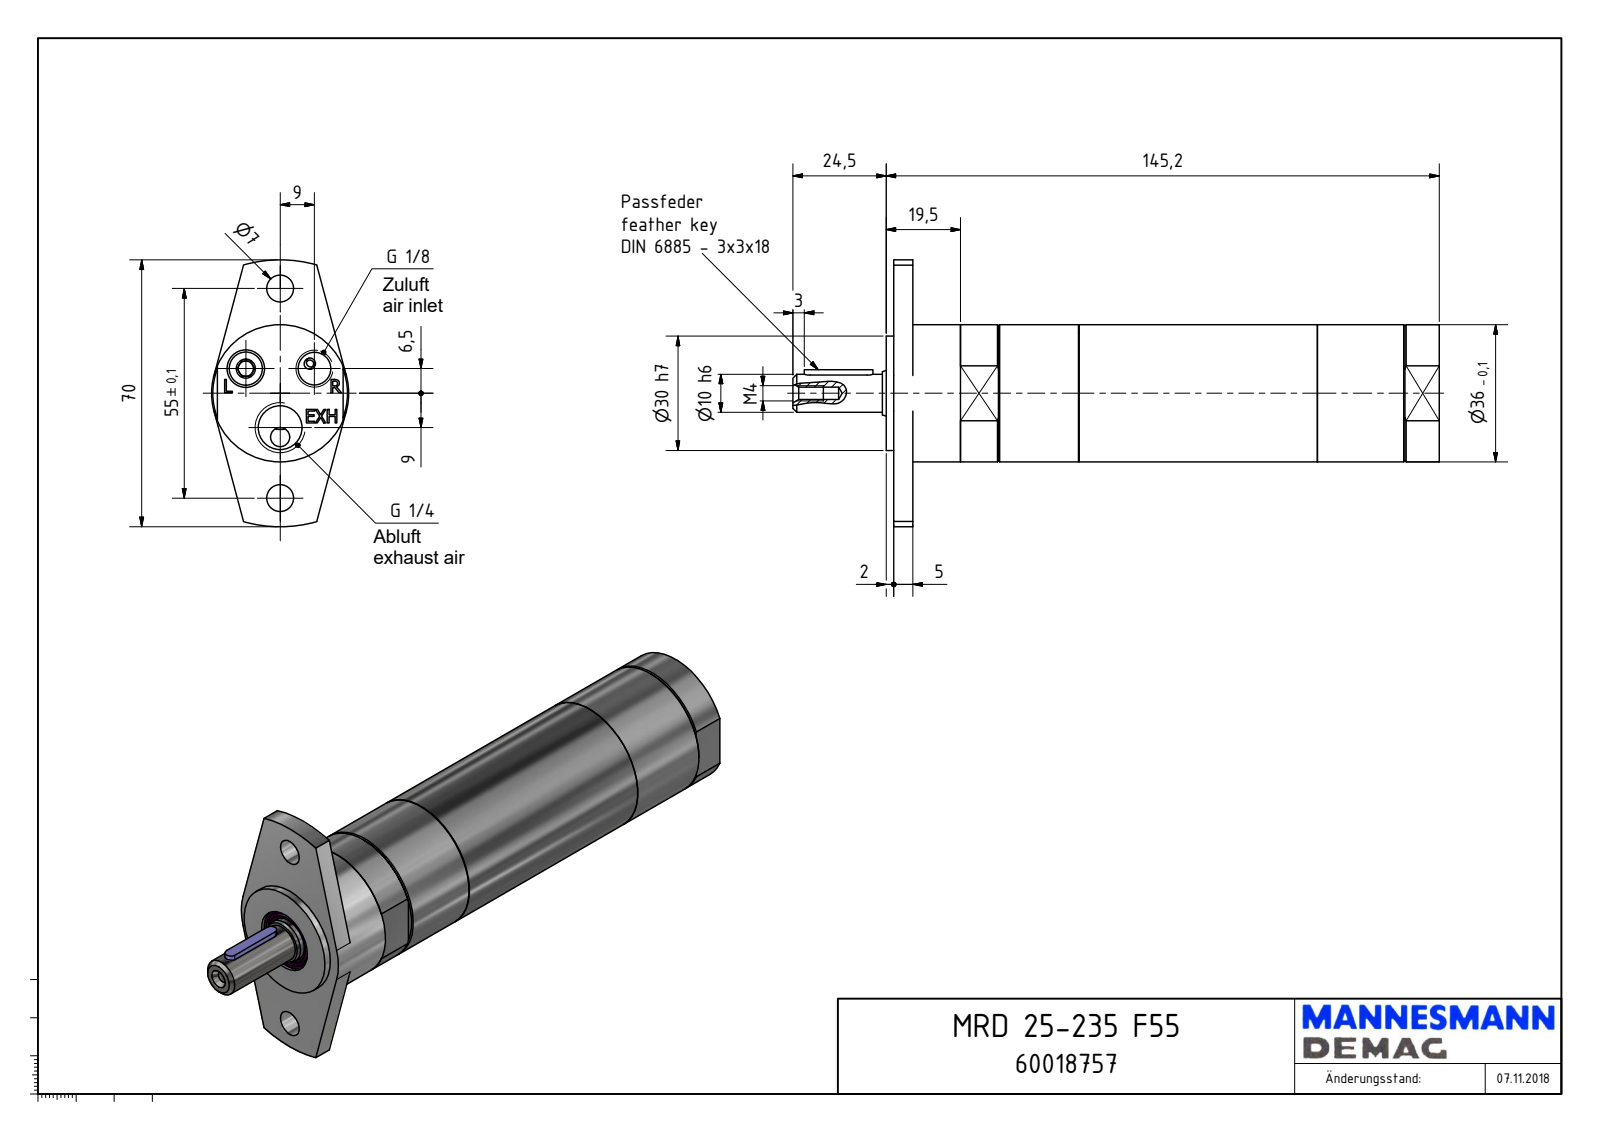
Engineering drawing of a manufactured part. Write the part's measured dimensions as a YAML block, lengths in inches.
part_name: "MRD 25-235 F55_60018757"
step_written_by: "Autodesk Inventor 2018 (AUTOMOTIVE_DESIGN)"
units: inches
bodies: {solids: 1, faces: 160, planar: 106, cylindrical: 27, other: 27}
overall_size: [6.681, 2.756, 1.417]
volume: 9.188
surface_area: 36.06
round_holes:
  - {diameter: 0.276, count: 2}
  - {diameter: 0.337, count: 2}
  - {diameter: 0.128, count: 1}
  - {diameter: 0.157, count: 1}
  - {diameter: 0.451, count: 1}
  - {diameter: 0.61, count: 1}
  - {diameter: 0.669, count: 1}
round_bosses_or_shafts:
  - {diameter: 1.417, count: 1}
  - {diameter: 1.26, count: 1}
  - {diameter: 1.181, count: 1}
  - {diameter: 0.47, count: 1}
  - {diameter: 0.394, count: 1}
partial_cylinders:
  - {radius: 0.059, count: 2}
  - {radius: 0.656, count: 1}
  - {radius: 1.378, count: 1}
face_to_face_distances: [0.197, 5.441, 5.638, 0.079, 0.276, 5.717, 1.299, 5.306, 5.228, 5.031]
hole_center_spacings: [0.437, 0.706, 0.9, 1.083, 1.385, 0.354, 0.709, 0.728]
